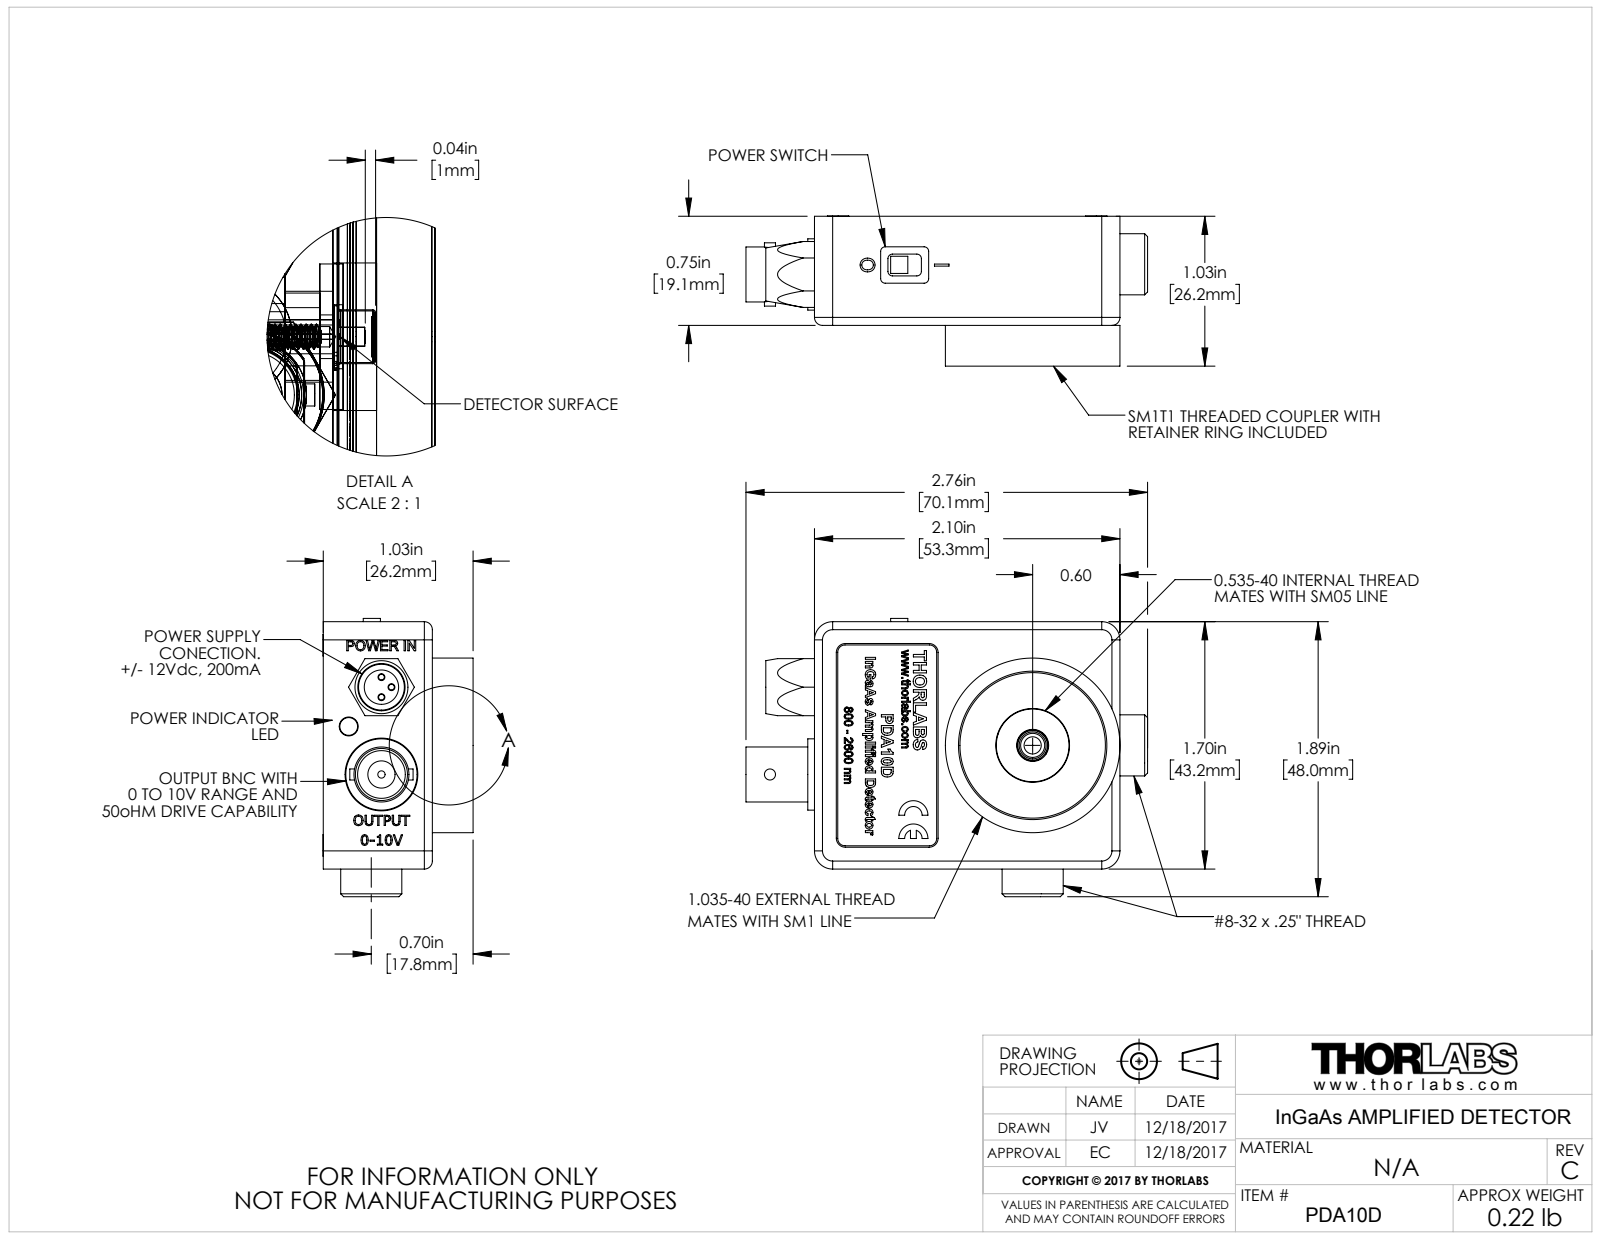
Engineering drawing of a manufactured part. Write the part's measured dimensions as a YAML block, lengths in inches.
part_name: "13127-E0W"
step_written_by: "SolidWorks 2009 (AUTOMOTIVE_DESIGN)"
units: inches
bodies: {solids: 20, faces: 1836, planar: 963, cylindrical: 281, other: 592}
overall_size: [2.761, 1.913, 1.031]
volume: 1.26
surface_area: 35.05
round_holes:
  - {diameter: 0.07, count: 7}
  - {diameter: 0.125, count: 4}
  - {diameter: 0.028, count: 3}
  - {diameter: 0.039, count: 3}
  - {diameter: 0.096, count: 3}
  - {diameter: 0.15, count: 3}
  - {diameter: 0.136, count: 2}
  - {diameter: 0.23, count: 2}
  - {diameter: 0.05, count: 1}
  - {diameter: 0.052, count: 1}
  - {diameter: 0.118, count: 1}
  - {diameter: 0.13, count: 1}
round_bosses_or_shafts:
  - {diameter: 0.086, count: 7}
  - {diameter: 0.02, count: 6}
  - {diameter: 0.147, count: 4}
  - {diameter: 0.14, count: 3}
  - {diameter: 0.018, count: 3}
  - {diameter: 0.42, count: 2}
  - {diameter: 0.236, count: 2}
  - {diameter: 1.2, count: 1}
partial_cylinders:
  - {radius: 0.125, count: 22}
  - {radius: 0.031, count: 12}
  - {radius: 0.01, count: 4}
  - {radius: 0.05, count: 4}
  - {radius: 0.055, count: 4}
  - {radius: 0.063, count: 4}
  - {radius: 0.095, count: 4}
  - {radius: 0.024, count: 2}
face_to_face_distances: [0.1, 0.063, 0.05, 0.07, 0.02, 0.215, 0.228, 0.165, 0.278, 0.298]
hole_center_spacings: [0.069, 0.1, 0.097, 0.141, 0.689, 0.736, 0.766, 0.788]
